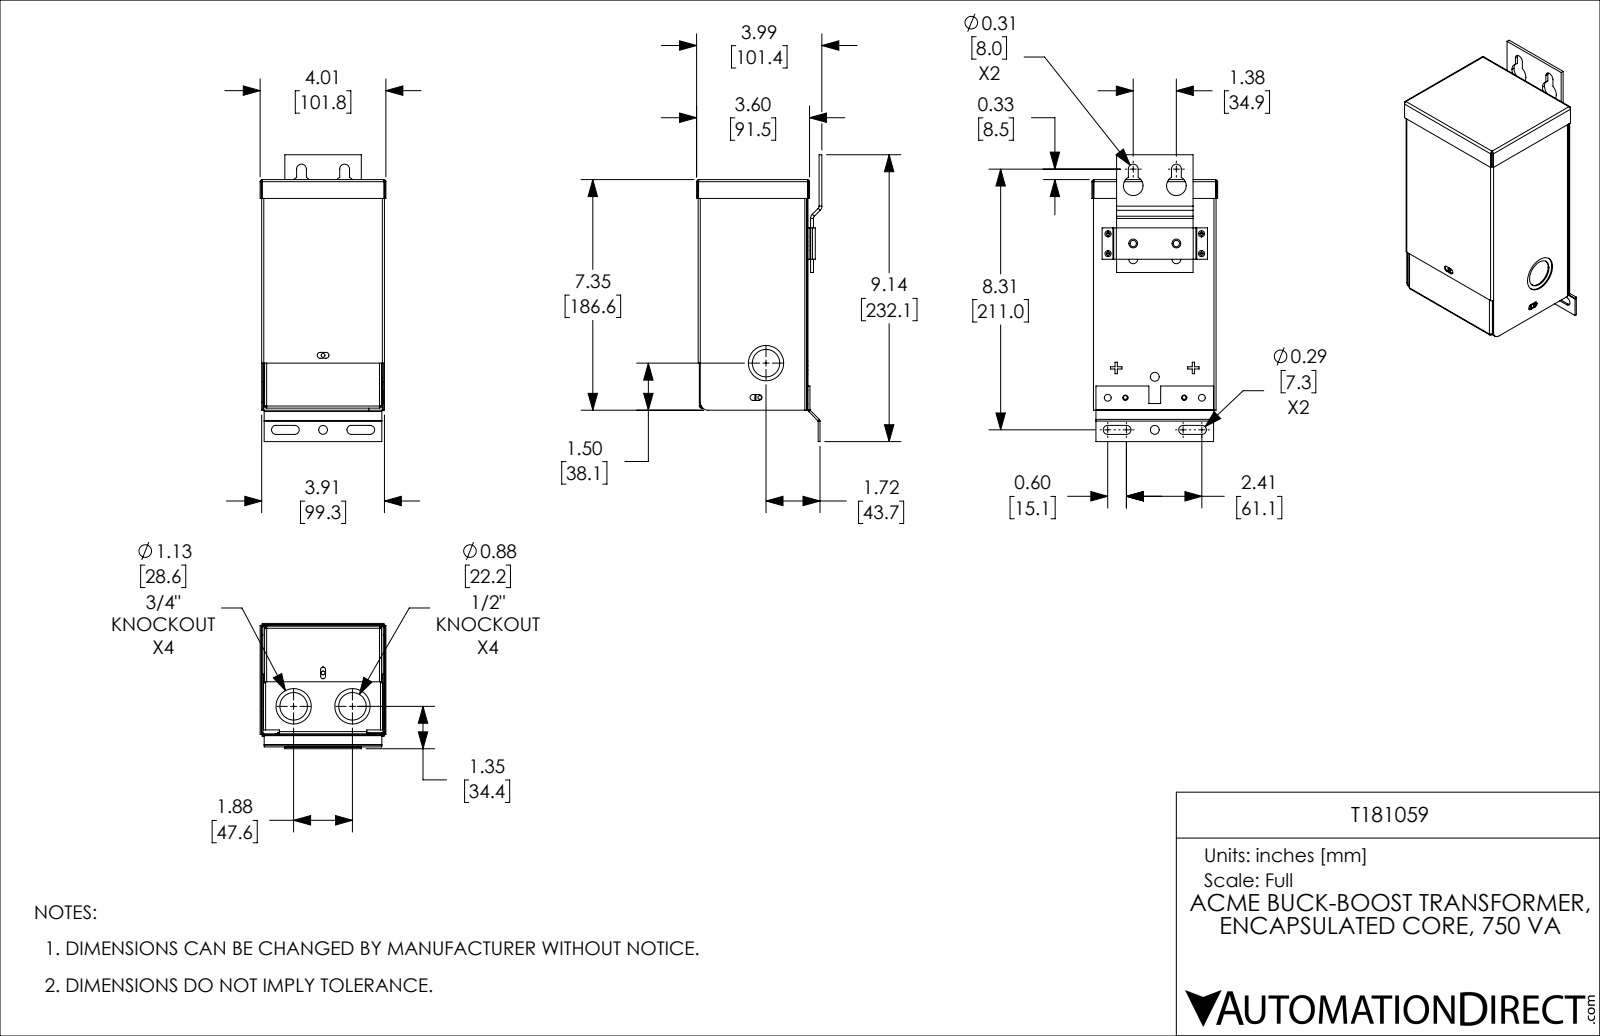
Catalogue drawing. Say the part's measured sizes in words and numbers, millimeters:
The part is named "T181059". Its 3-D file was written by "SolidWorks 2021 (CONFIG_CONTROL_DESIGN)". It is 7 solids with 528 faces: 326 planar, 154 cylindrical and 48 other. Overall it measures 232.07 by 101.8 by 101.43 millimeters. Its volume is 113 073 cubic millimeters and its surface area 227 401 square millimeters. Round holes: 5 of diameter 3.05, 3 of diameter 7.14, 3 of diameter 7.14, 3 of diameter 22.22, 3 of diameter 28.57, 2 of diameter 4.34, 2 of diameter 4.76, 2 of diameter 5.11, 2 of diameter 5.54, 2 of diameter 15.88, 1 of diameter 28.58. Round bosses or shafts: 3 of diameter 30.4, 3 of diameter 24.05. Partial cylindrical surfaces (rounded edges, fillets, slot ends): 16 of radius 0.79, 16 of radius 1.7, 8 of radius 2.38, 4 of radius 0.66, 4 of radius 2.18, 4 of radius 3.66, 2 of radius 0.43, 2 of radius 1.96. The main face-to-face distances are 0.91, 87.99, 98.41, 87.08, 99.32, 97.5, 88.9, 1.53, 183.95, 182.42. The hole center spacings are 34.92, 12.7, 12.74, 14.27, 14.29, 29.09, 29.23, 34.94.
